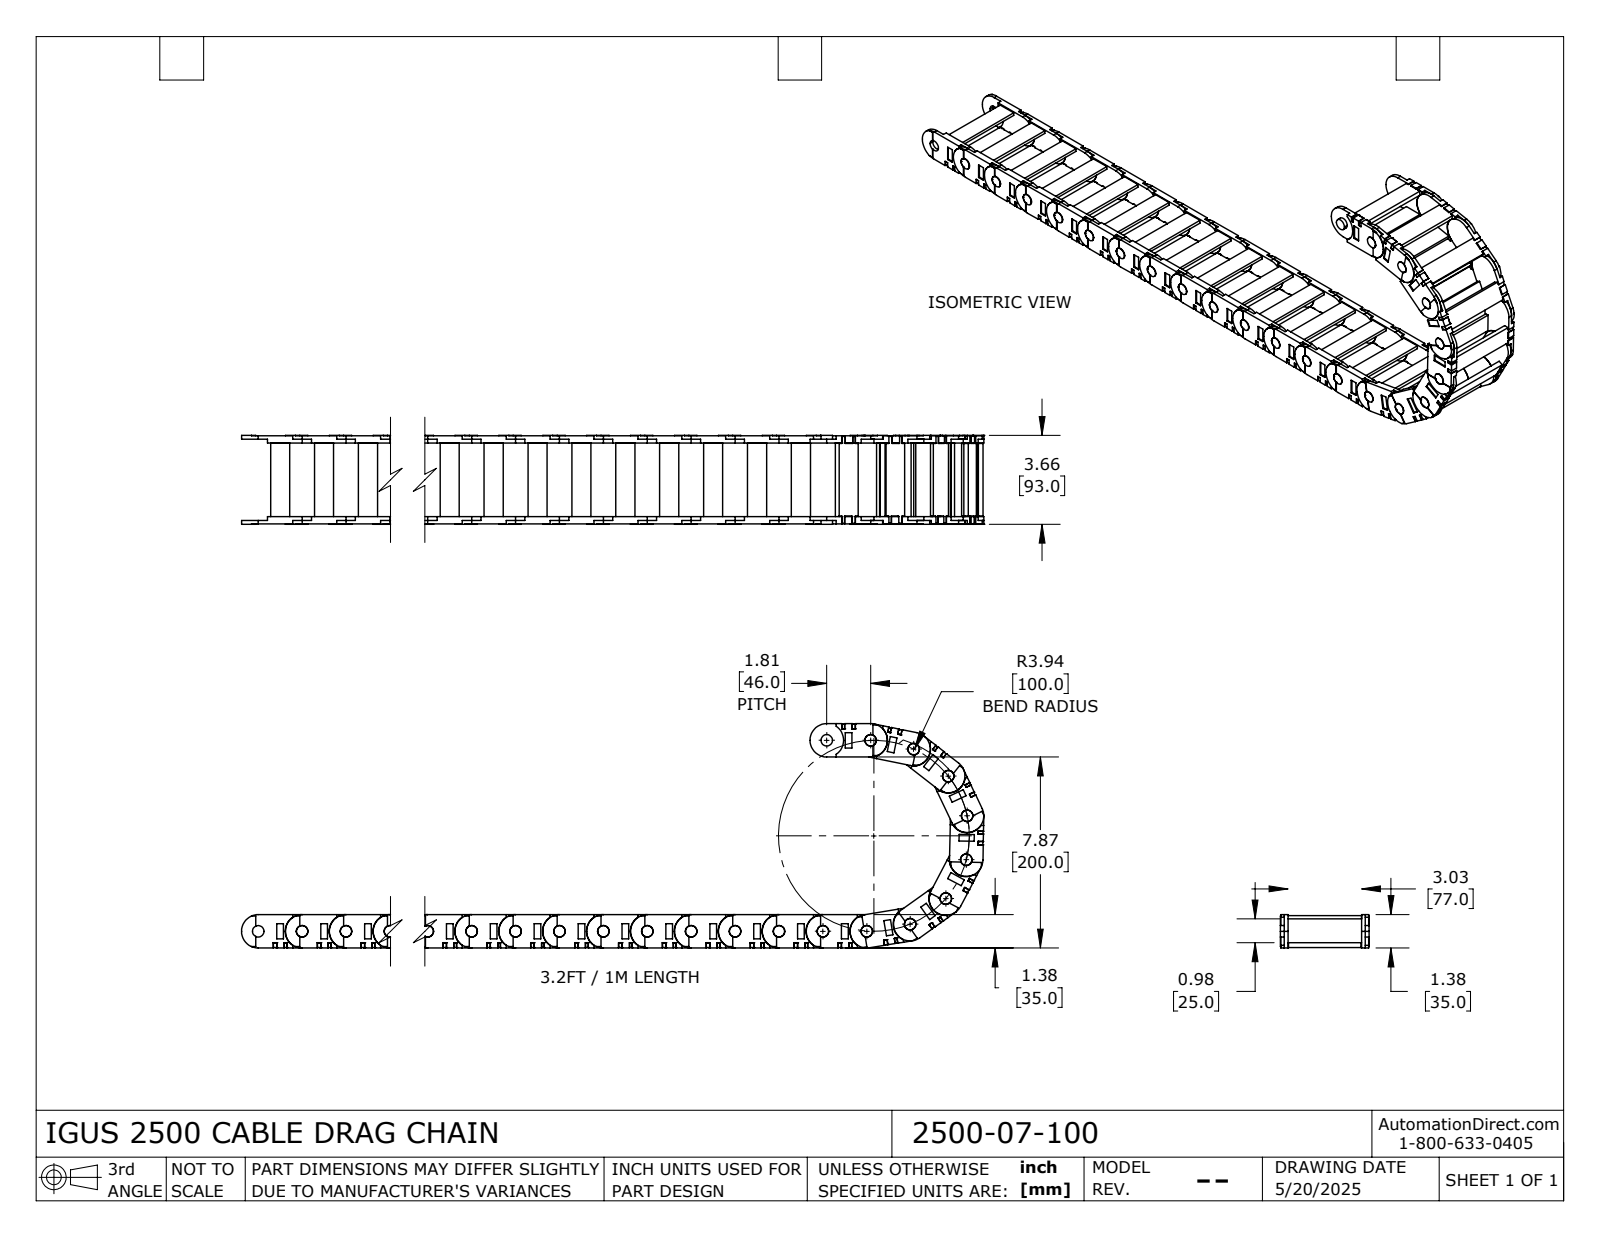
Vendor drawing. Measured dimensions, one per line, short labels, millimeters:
name: 2500_07_100
written by: SolidWorks 2024 (AUTOMOTIVE_DESIGN)
unit: mm
bodies: 66 solids, 2398 faces (1870 planar, 528 cylindrical, 0 other)
size: 784.1 × 235 × 93
volume: 814 300 mm³; area: 470 900 mm²
holes: 22× ⌀12
bosses: 22× ⌀12, 21× ⌀35
rounds: 23× R17.7, 2× R17.5
face distances: 4, 81, 85, 3.6, 7.6, 84.6, 88.6, 77, 3.4, 5
hole spacings: 46, 92, 138, 184, 230, 276, 322, 368
